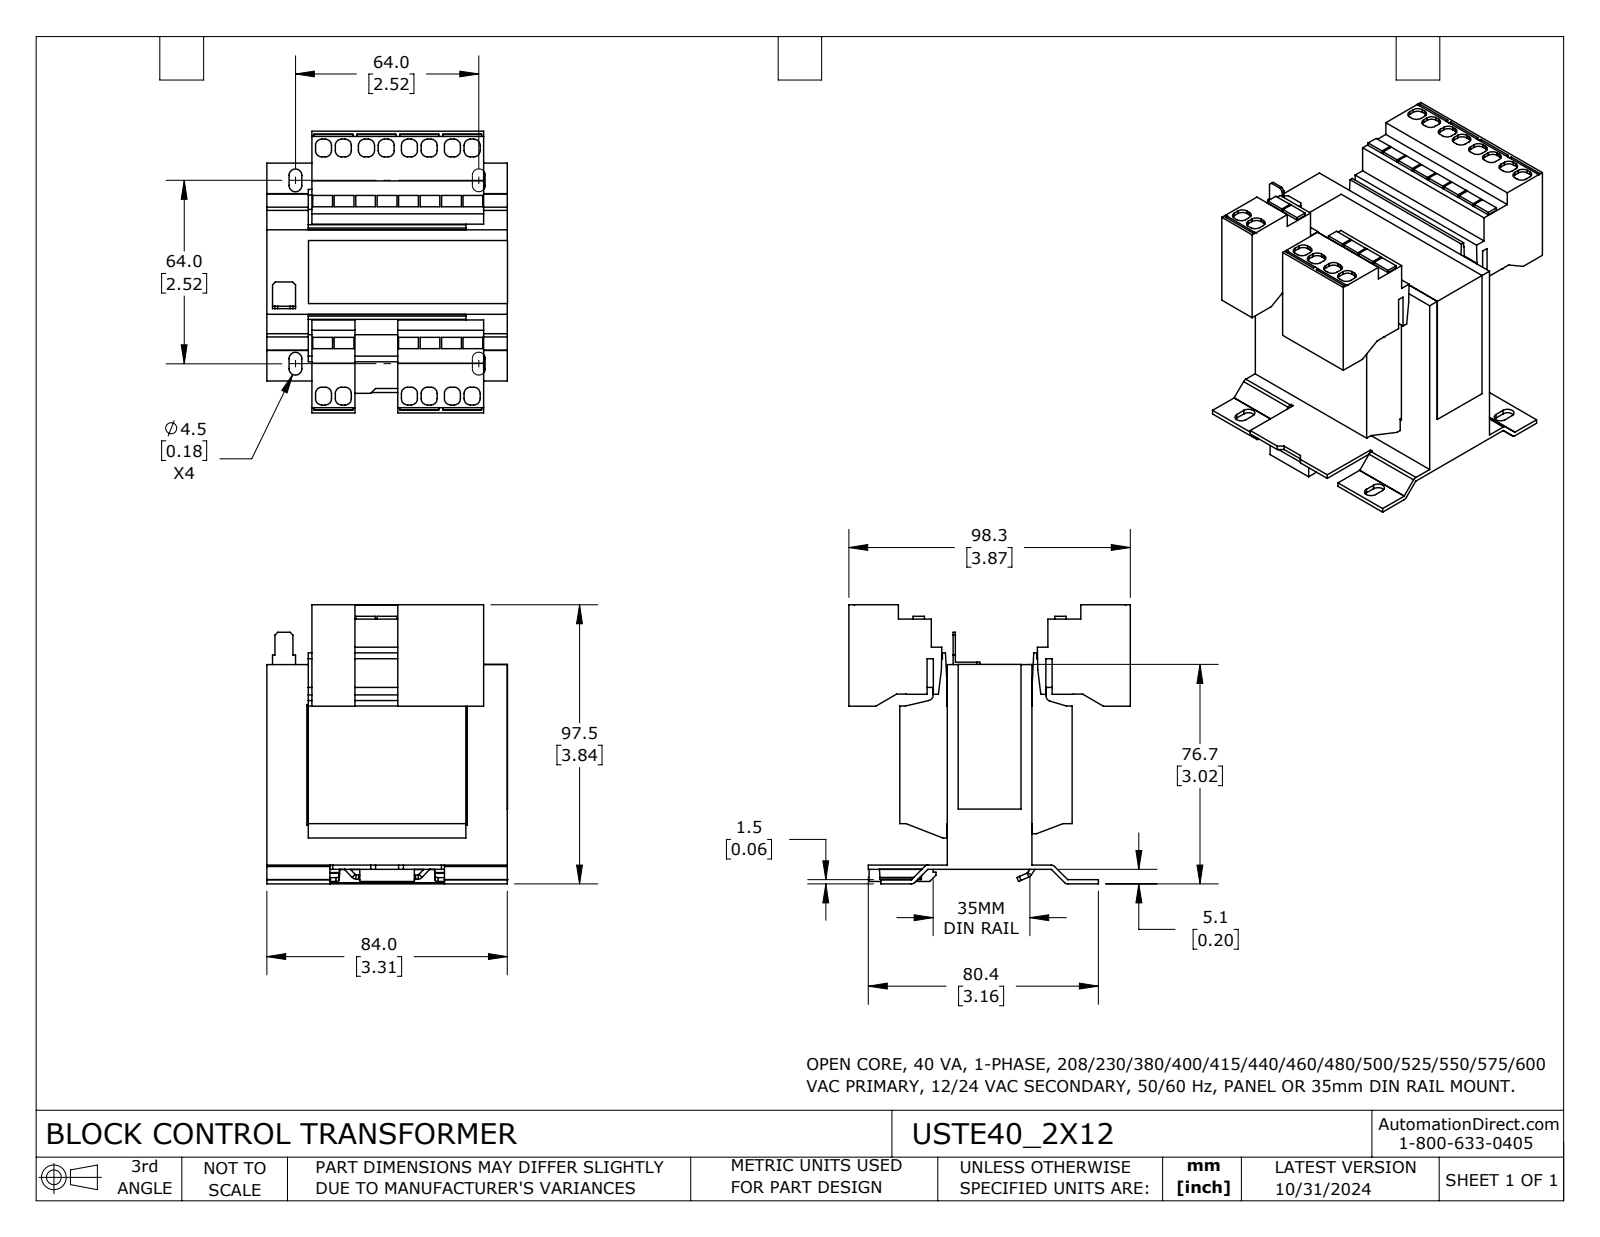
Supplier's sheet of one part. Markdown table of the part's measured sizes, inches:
| quantity | value |
| --- | --- |
| part name | USTE40_2X12 |
| STEP written by | SolidWorks 2023 (CONFIG_CONTROL_DESIGN) |
| units | inches |
| bodies | 1 solid, 595 faces (483 planar, 100 cylindrical, 12 other) |
| overall size | 3.87 × 3.837 × 3.309 |
| volume | 21.09 in³ |
| surface area | 121.3 in² |
| partial cylindrical surfaces (radius × count) | 0.087 × 56, 0.079 × 9, 0.089 × 8, 0.004 × 4, 0.039 × 4, 0.063 × 4, 0.02 × 3 |
| main face-to-face distances | 0.039, 0.551, 0.059, 2.736, 0.571, 2.476, 2.756, 1.354, 2.516, 1.161 |
